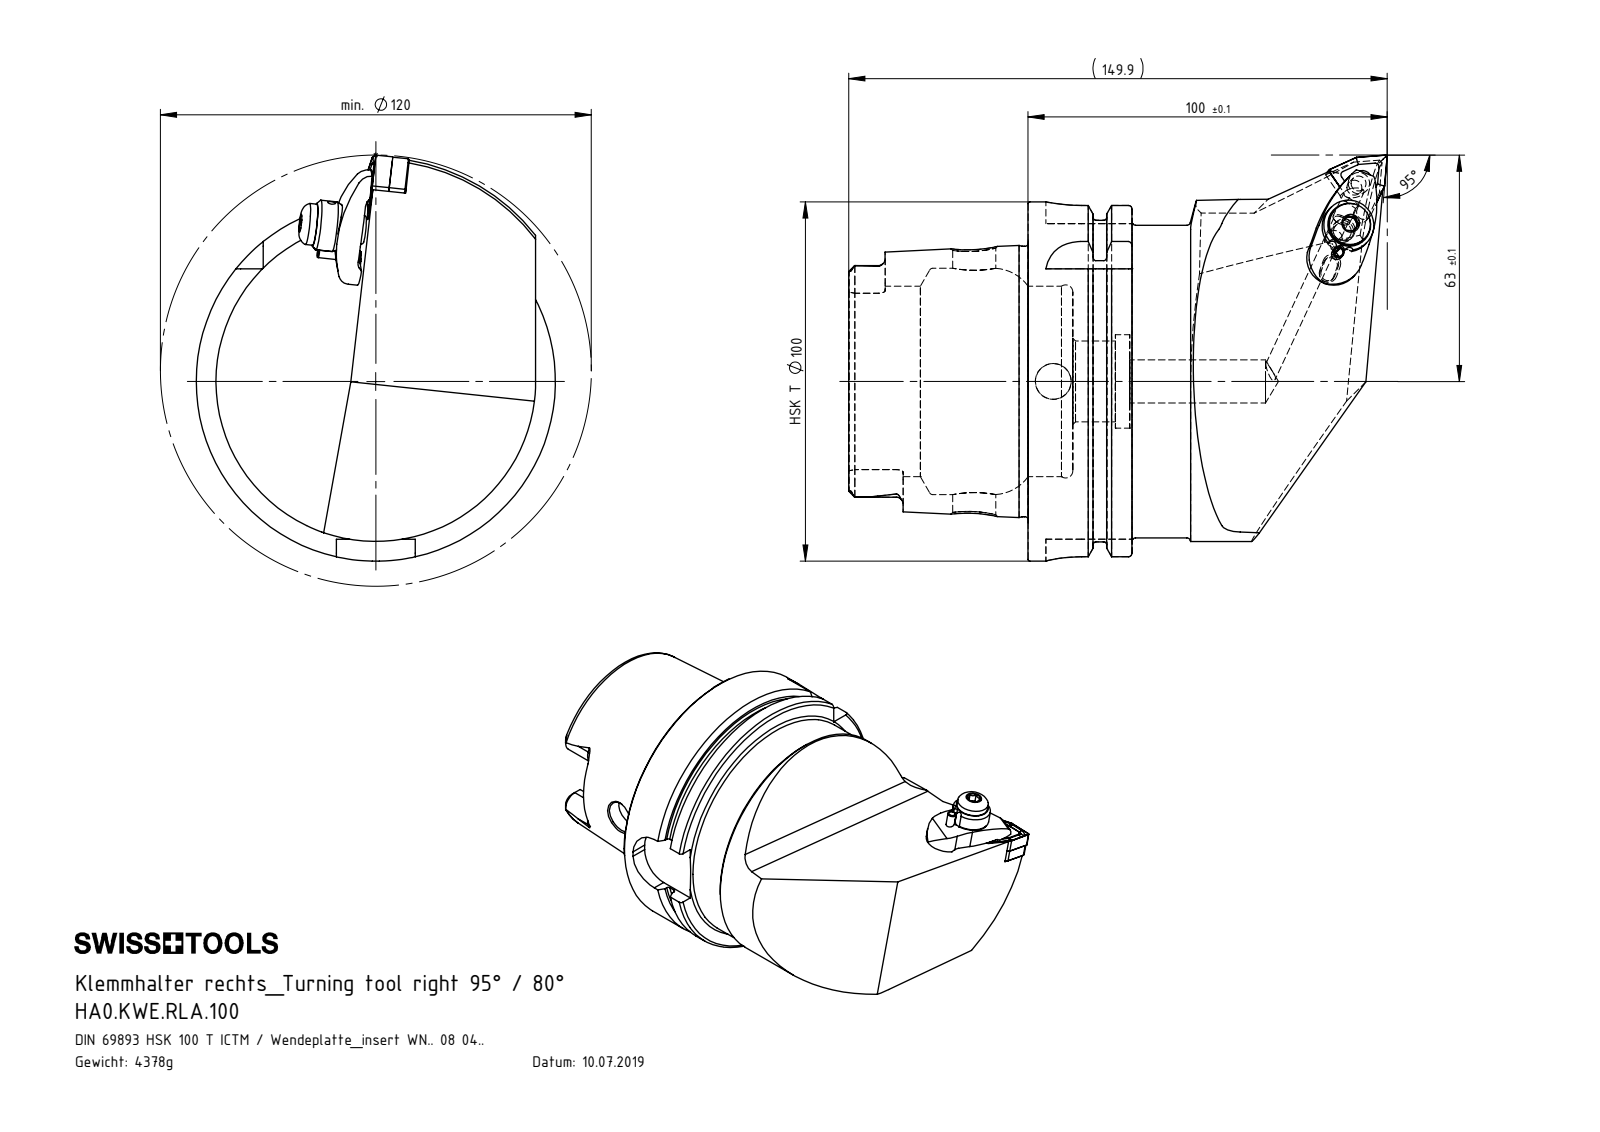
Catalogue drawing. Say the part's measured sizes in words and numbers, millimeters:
The part is named "ISO 13337 - 3 x 12_PreviewCfg; WWE-ER2.101.004_A; WCC-ER5.102.005_A; WCC-ER3.102.024_C (+7 more)". Its 3-D file was written by "SolidWorks 2017 (AUTOMOTIVE_DESIGN)". It is 11 solids with 489 faces: 133 planar, 158 cylindrical and 198 other. Overall it measures 149.9 by 113 by 100 millimeters. Its volume is 546 099 cubic millimeters and its surface area 73 864 square millimeters. Round holes: 3 of diameter 2, 2 of diameter 4.2, 2 of diameter 5, 2 of diameter 7, 2 of diameter 12, 1 of diameter 2.4, 1 of diameter 3, 1 of diameter 4, 1 of diameter 5.16, 1 of diameter 6.2, 1 of diameter 6.7, 1 of diameter 7.8. Round bosses or shafts: 2 of diameter 5, 1 of diameter 100, 1 of diameter 91.95, 1 of diameter 87, 1 of diameter 75.26, 1 of diameter 14, 1 of diameter 11.5, 1 of diameter 7. Partial cylindrical surfaces (rounded edges, fillets, slot ends): 6 of radius 0.39, 6 of radius 0.69, 6 of radius 1.9, 4 of radius 0.4, 4 of radius 10, 3 of radius 1.5, 3 of radius 2, 2 of radius 3. The main face-to-face distances are 12.45, 16.5, 28.95, 49.9, 62.35, 78.85, 87.8, 78.2, 28.3, 15.85. The hole center spacings are 15, 14.8, 23, 8, 8.01, 8.2, 14.99.
